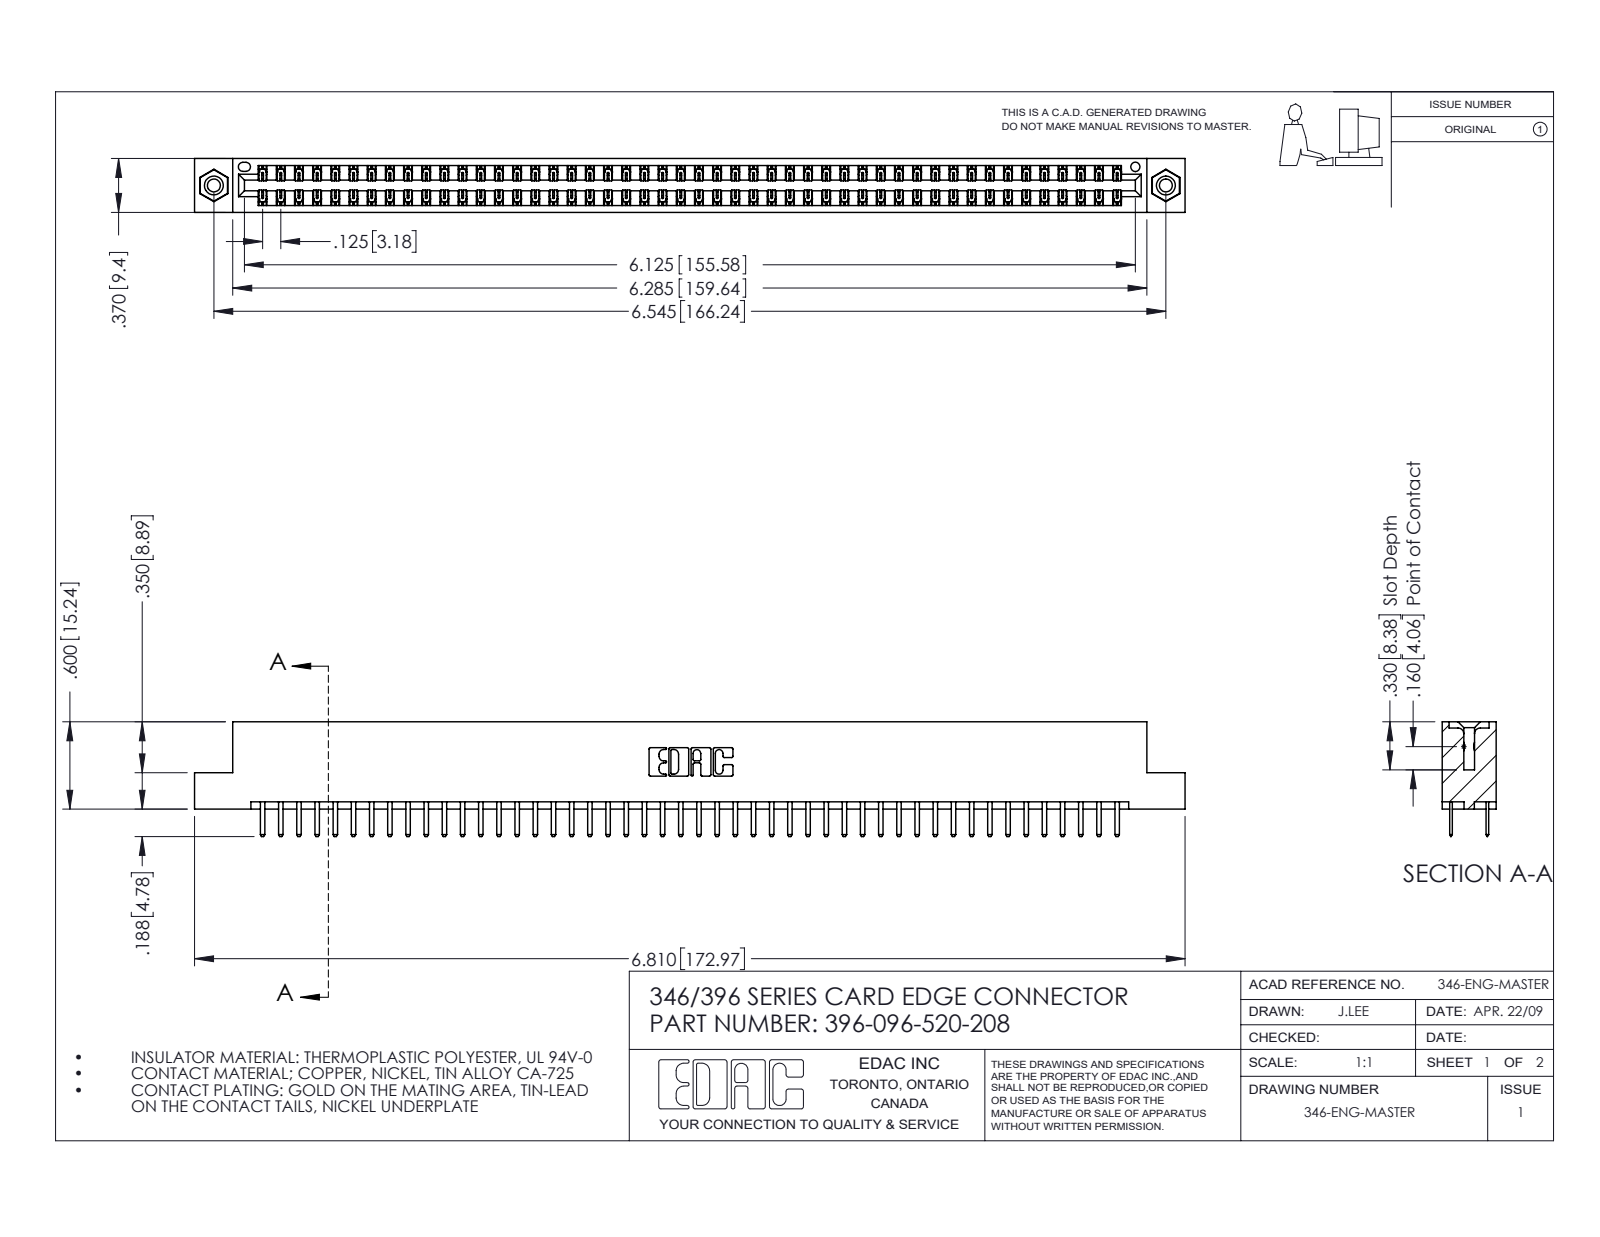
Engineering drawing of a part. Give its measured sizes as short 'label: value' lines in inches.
name: 396-096-520-208; 345-250-001_345-250-003-102; 346 Part_Flush Mounting Lugs - 0.156 Dia-TI; 345-292-001_345-293-120
written by: SolidWorks 2016 (CONFIG_CONTROL_DESIGN)
unit: in
bodies: 99 solids, 5558 faces (3660 planar, 1882 cylindrical, 16 other)
size: 6.81 × 0.788 × 0.37
volume: 1.029 in³; area: 35.96 in²
holes: 2× ⌀0.089, 2× ⌀0.125, 2× ⌀0.156, 1× ⌀0.064
bosses: 2× ⌀0.155
rounds: 144× R0.006, 100× R0.01, 22× R0.01, 6× R0.007, 6× R0.031, 3× R0.026, 2× R0.014, 2× R0.022
face distances: 0.048, 0.322, 0.25, 0.37, 0.275, 0.072, 0.298, 0.025, 0.148, 0.222
hole spacings: 0.246, 6.336, 6.545
